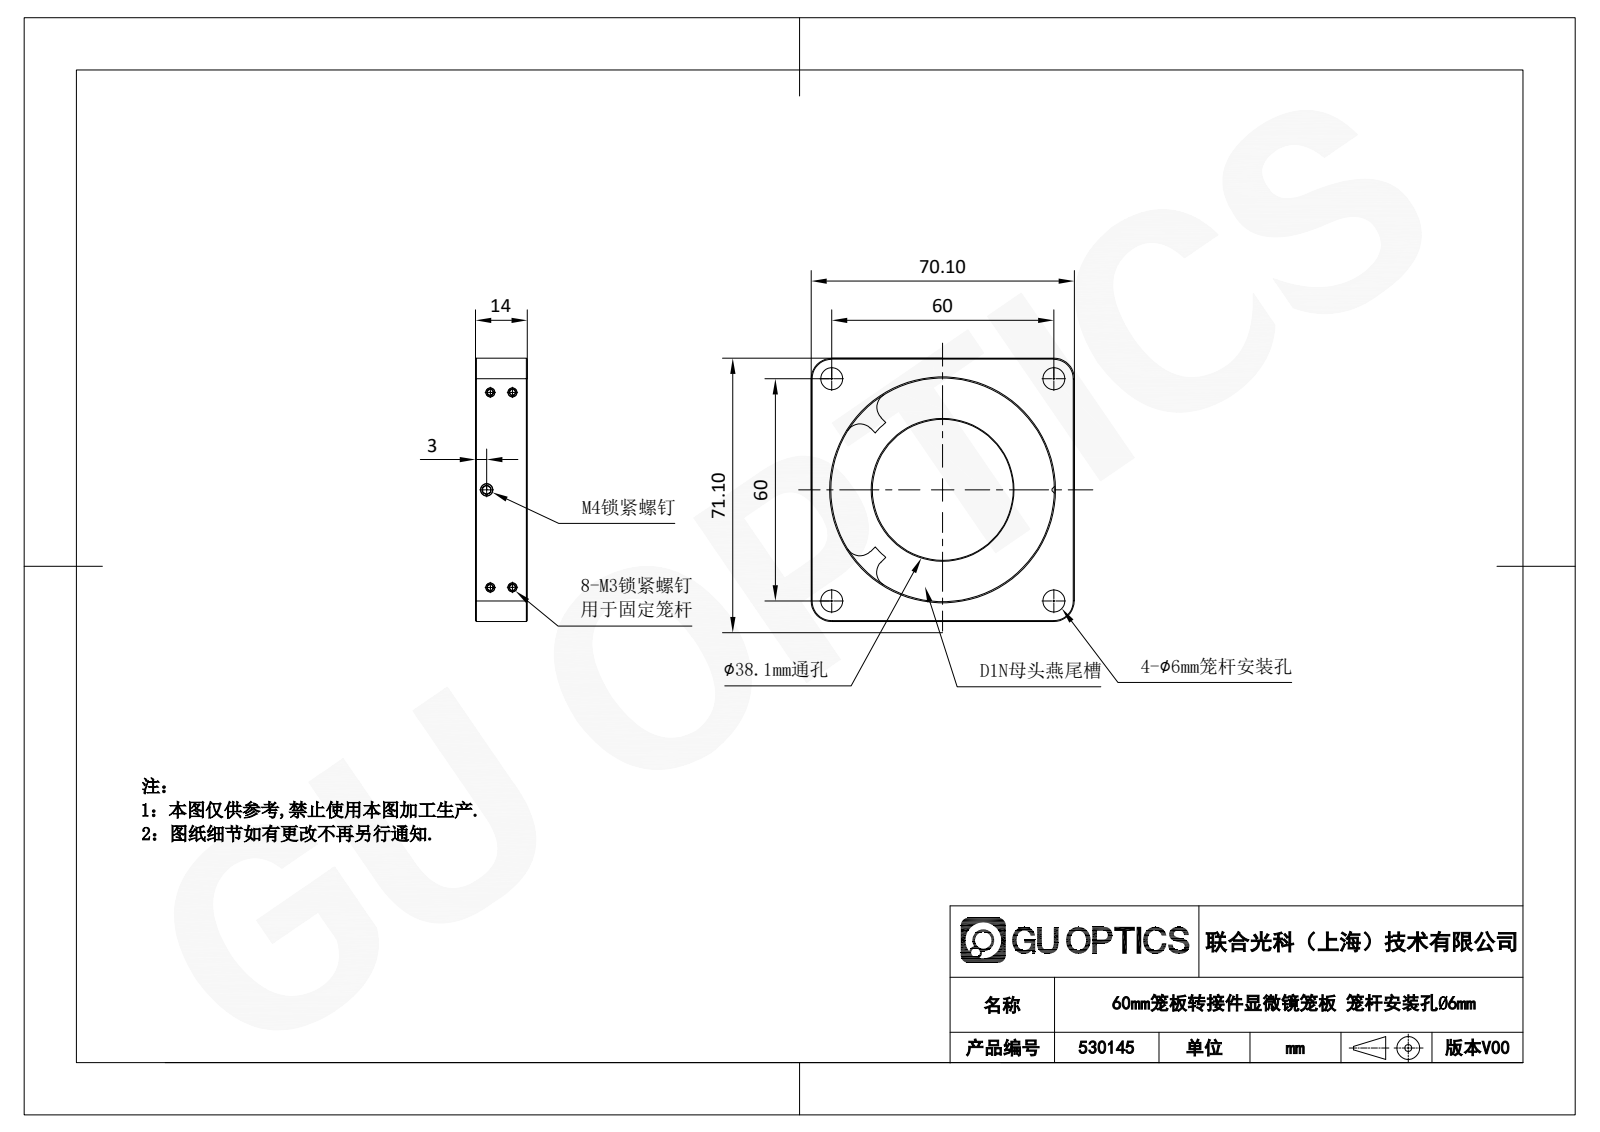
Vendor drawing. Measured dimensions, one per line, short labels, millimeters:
name: 530145
written by: SolidWorks 2020 (CONFIG_CONTROL_DESIGN)
unit: mm
bodies: 10 solids, 237 faces (108 planar, 36 cylindrical, 93 other)
size: 71.12 × 71.12 × 13.97
volume: 40 828 mm³; area: 15 483 mm²
holes: 4× ⌀2.5, 4× ⌀6.02, 1× ⌀3.3, 1× ⌀38.1, 1× ⌀60.5
bosses: 4× ⌀3, 1× ⌀4
rounds: 4× R3.97, 4× R5.55, 1× R23.84
face distances: 13.97, 7.01, 6.96, 71.12, 0.99, 6.02, 12.98, 59.81, 1.5, 6.76
hole spacings: 42.43, 60, 6, 26.37, 27.26, 52.7, 53.04, 84.85
